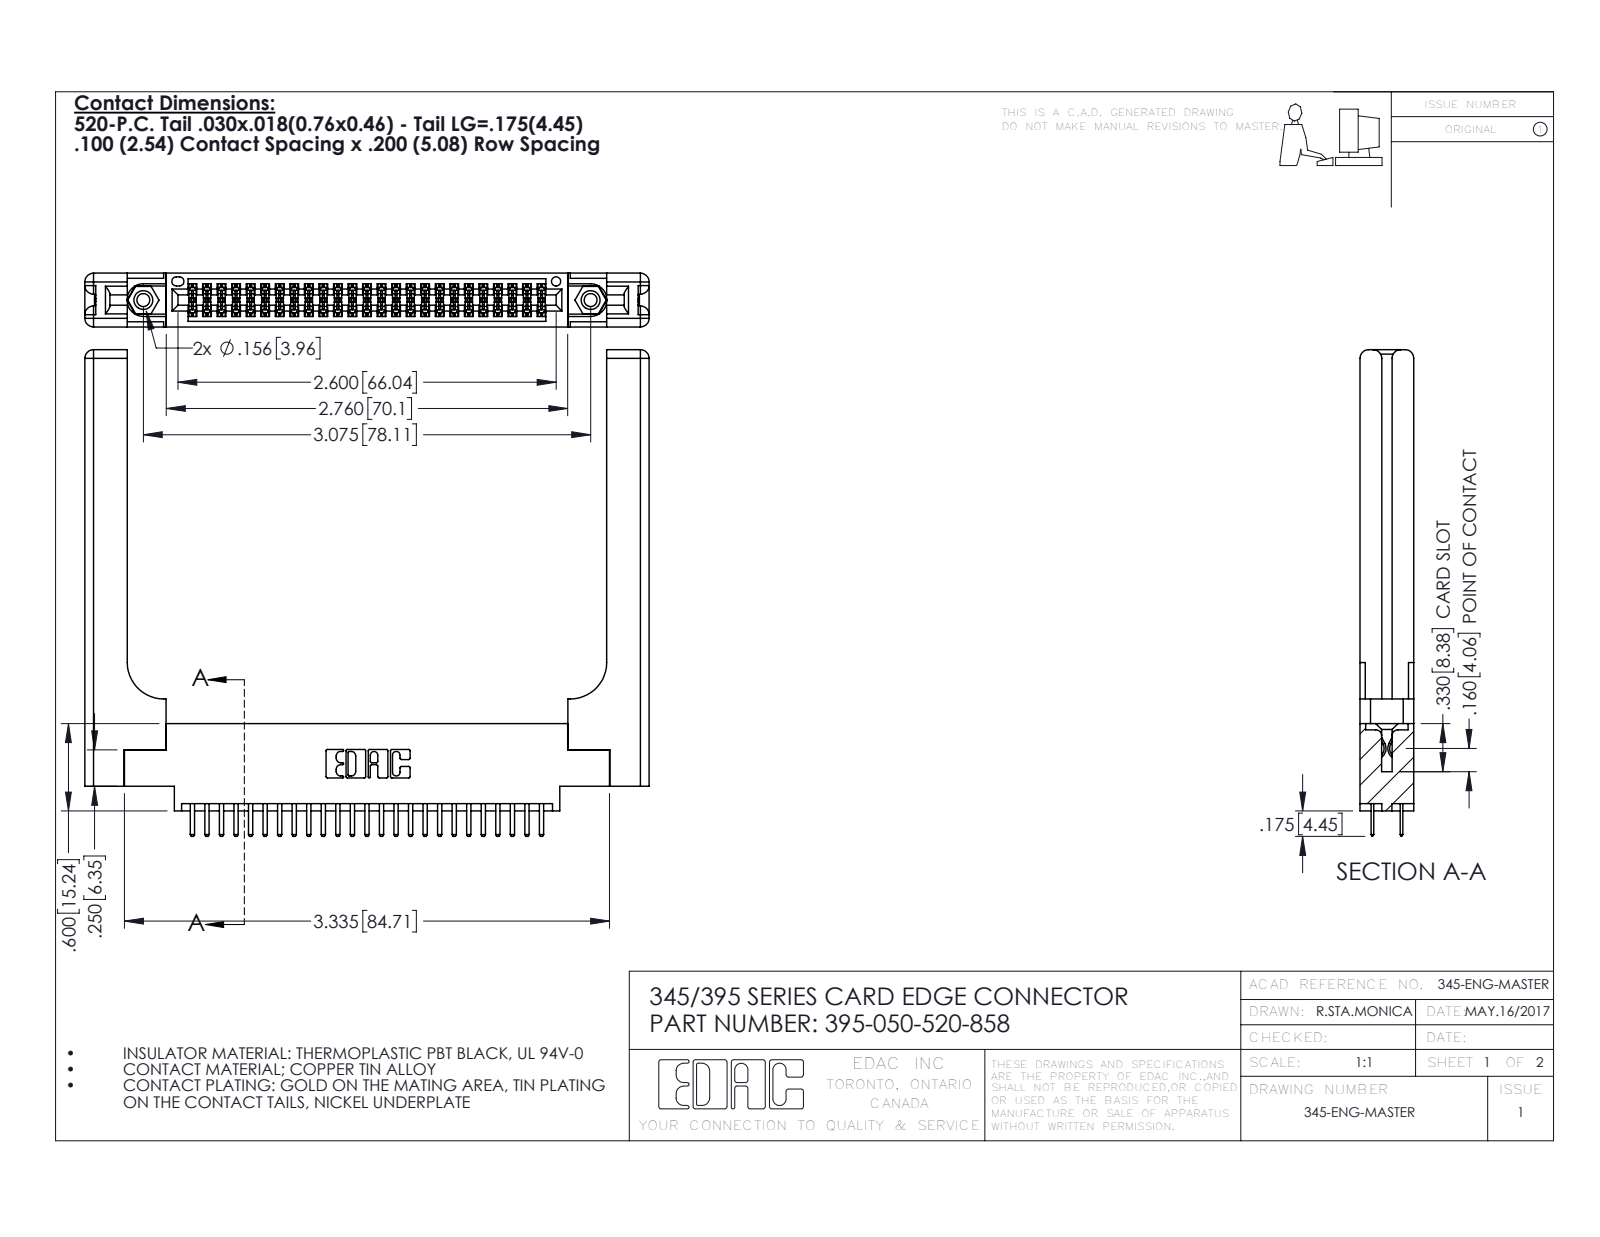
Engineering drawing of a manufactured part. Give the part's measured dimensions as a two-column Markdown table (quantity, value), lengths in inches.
| quantity | value |
| --- | --- |
| part name | 345-250-001_345-250-001-102; 345 Part_0.170 Offset - 0.156 Dia-TH; 345-292-001_345-293-120; 345-220-058_345-220-058 (+1 more) |
| STEP written by | SolidWorks 2016 (CONFIG_CONTROL_DESIGN) |
| units | inches |
| bodies | 55 solids, 3086 faces (1982 planar, 1044 cylindrical, 60 other) |
| overall size | 3.879 × 3.345 × 0.37 |
| volume | 1.083 in³ |
| surface area | 28.74 in² |
| round holes (diameter × count) | 0.089 × 2, 0.125 × 2, 0.156 × 2, 0.064 × 1 |
| round bosses / shafts (diameter × count) | 0.155 × 2 |
| partial cylindrical surfaces (radius × count) | 0.006 × 75, 0.01 × 54, 0.01 × 22, 0.06 × 16, 0.007 × 6, 0.031 × 6, 0.026 × 3, 0.014 × 2 |
| main face-to-face distances | 0.37, 0.072, 0.298, 0.2, 0.148, 0.15, 0.098, 0.272, 0.025, 0.225 |
| hole center spacings | 0.27, 2.84, 3.075 |
